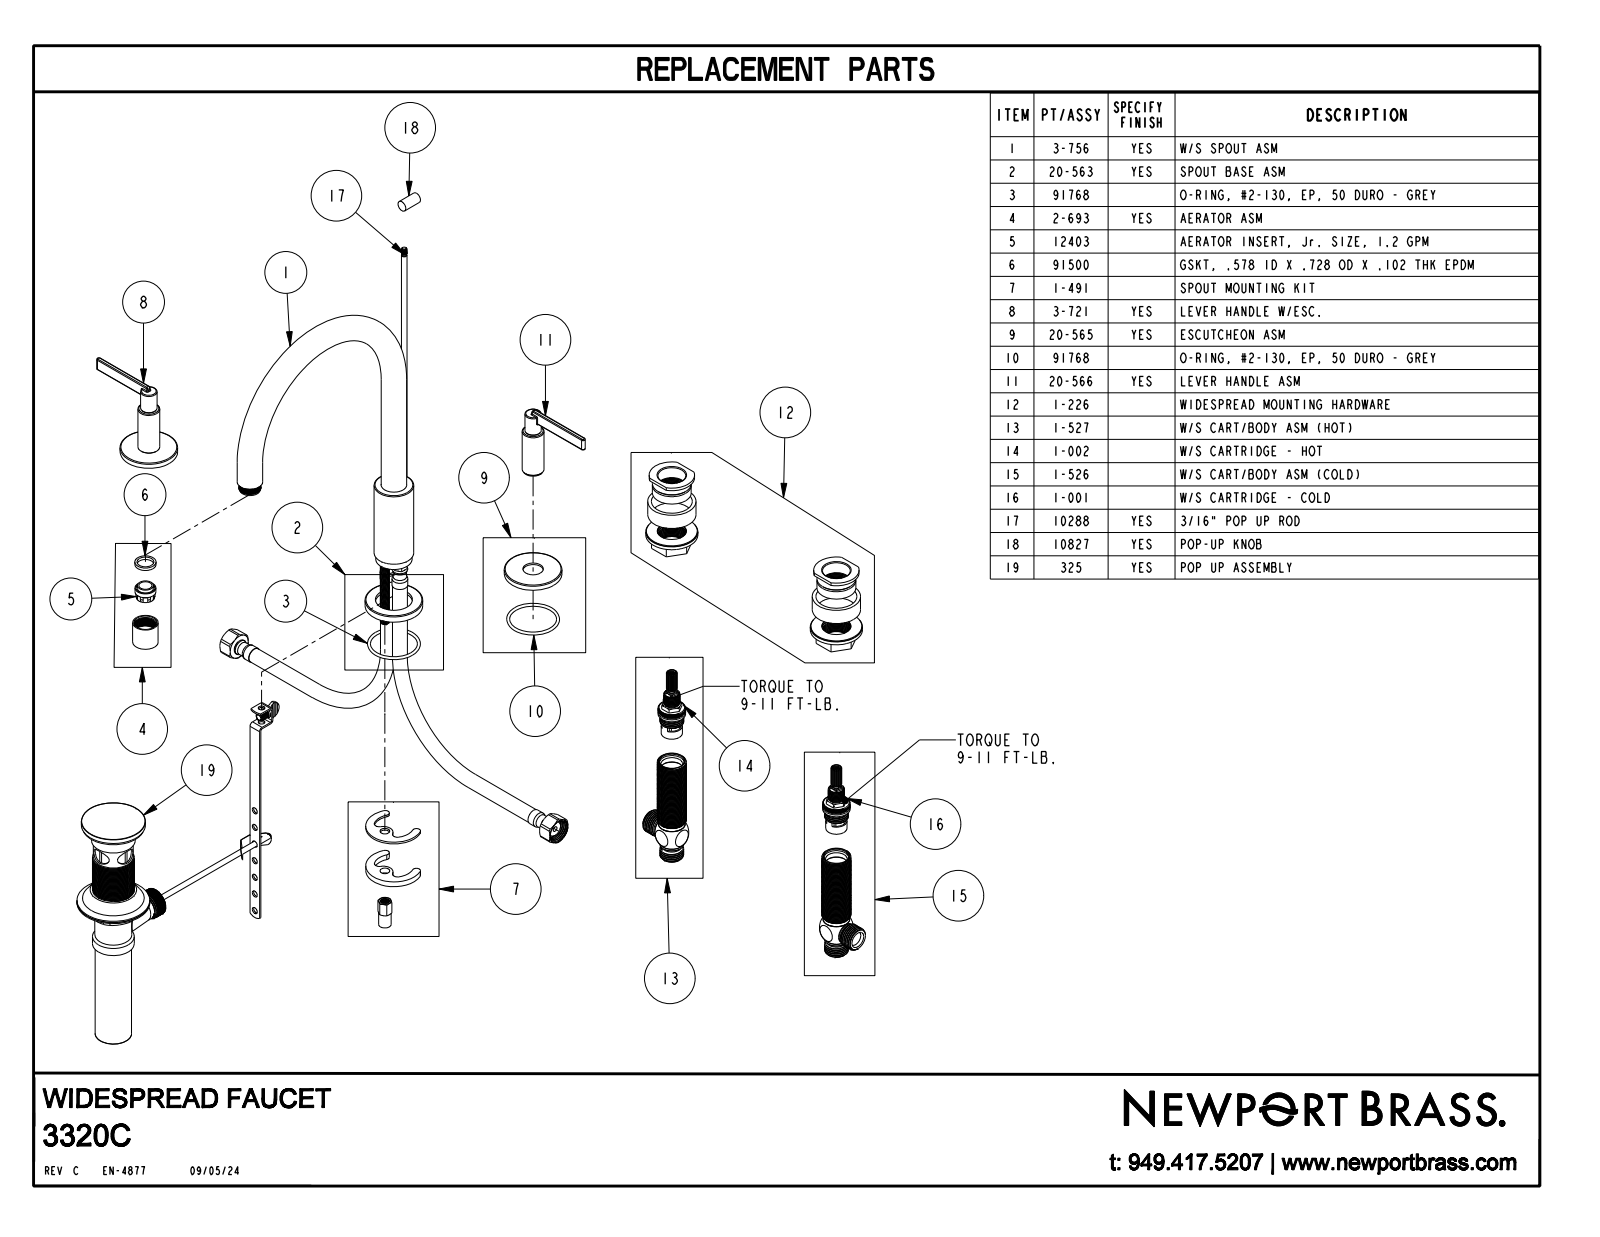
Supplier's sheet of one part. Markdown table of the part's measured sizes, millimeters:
| quantity | value |
| --- | --- |
| part name | 3320C_SW |
| STEP written by | CREO PARAMETRIC BY PTC INC, 2023134 (CONFIG_CONTROL_DESIGN) |
| units | millimeters |
| bodies | 6 solids, 199 faces (57 planar, 94 cylindrical, 48 other) |
| overall size | 330.2 × 291.9 × 216.9 |
| volume | 299 400 mm³ |
| surface area | 66 060 mm² |
| round holes (diameter × count) | 13.6 × 2, 14.2 × 1, 15.7 × 1, 17.6 × 1 |
| round bosses / shafts (diameter × count) | 50.3 × 3, 22.2 × 2, 19.1 × 2, 18.5 × 2, 14.3 × 2, 13 × 2, 34.5 × 1, 11.8 × 1 |
| partial cylindrical surfaces (radius × count) | 0.8 × 16, 1.5 × 2, 1.9 × 2, 5 × 2, 8.6 × 1 |
| main face-to-face distances | 5.1, 1.3, 3.8, 6.4, 79.4, 74.3, 73, 6.7, 10.5, 39.9 |
| hole center spacings | 204.8, 203.2 |
